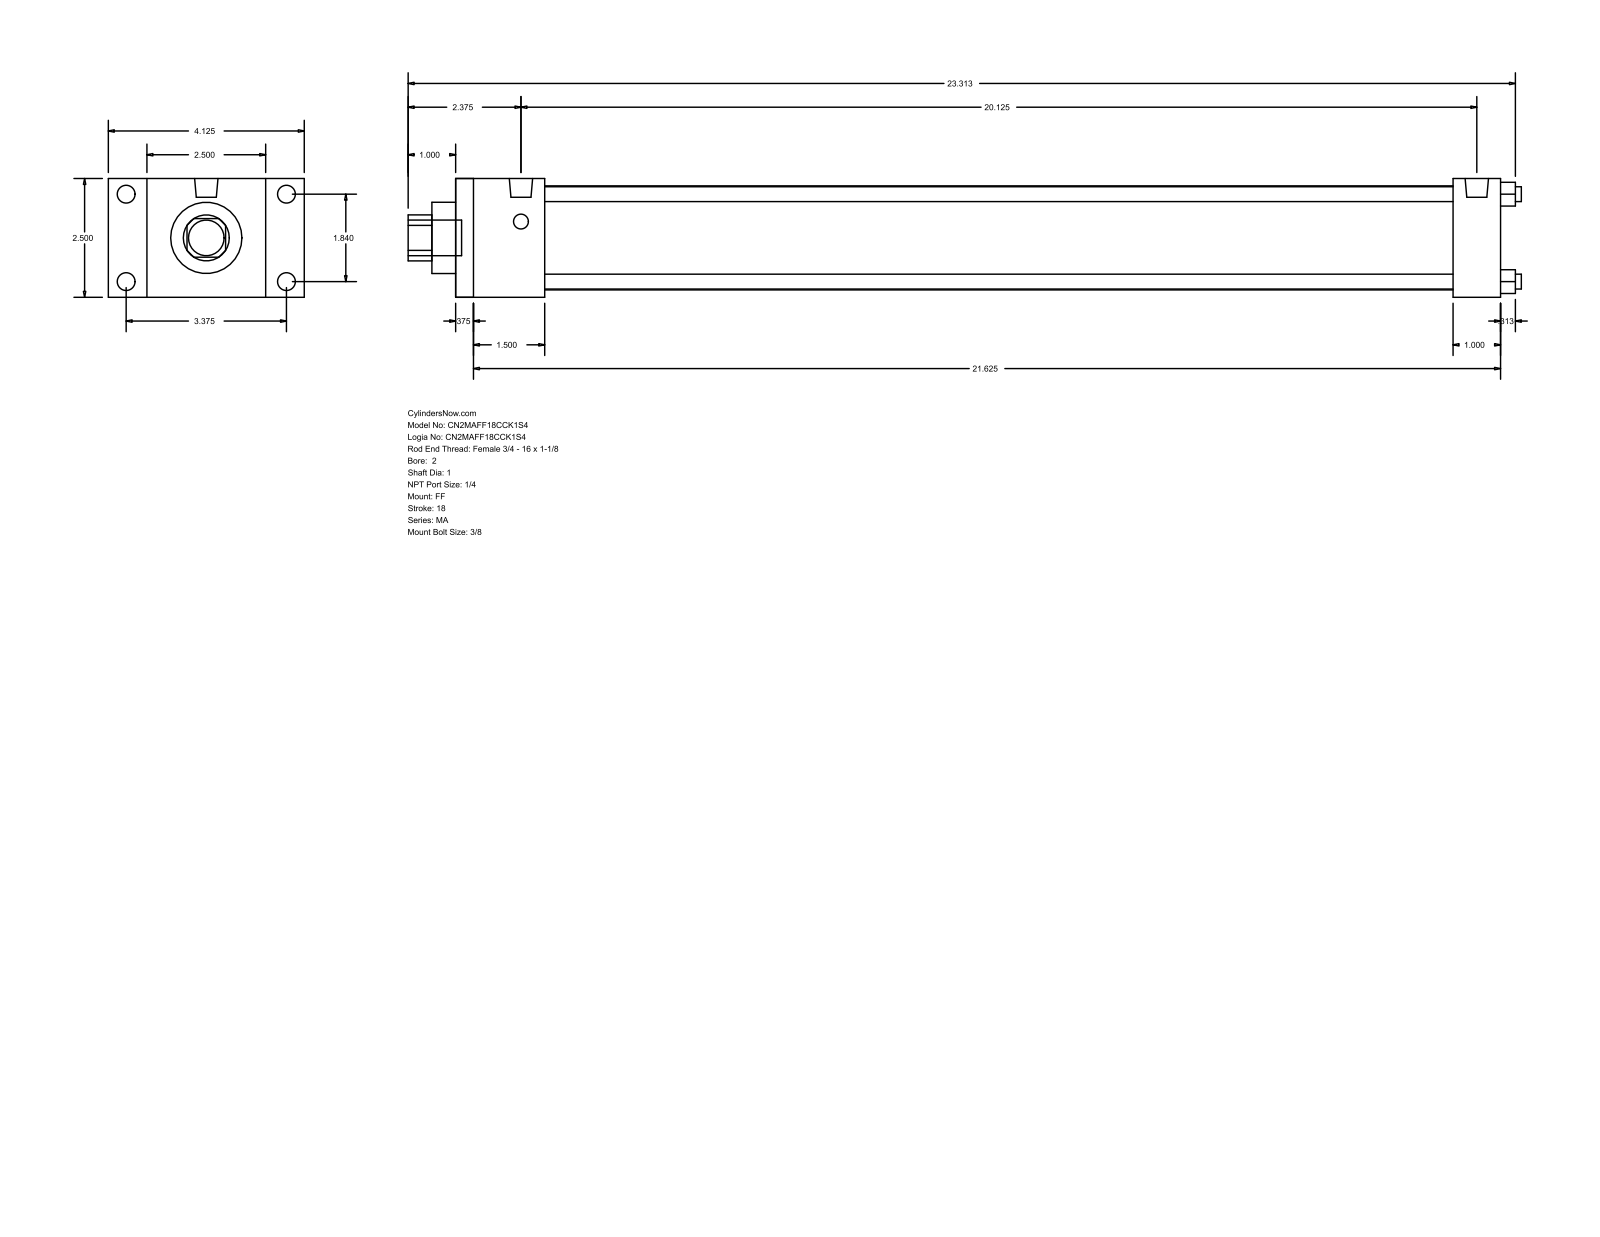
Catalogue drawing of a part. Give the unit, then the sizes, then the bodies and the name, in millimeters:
Units: millimetres
Overall size (bounding box): 595.31 × 104.78 × 63.5
Round holes (diameter × count): ⌀7.94 ×4, ⌀25.4 ×1, ⌀38.1 ×1, ⌀55.63 ×1
Round bosses / shafts (diameter × count): ⌀9.53 ×4, ⌀7.94 ×4, ⌀12.49 ×2, ⌀19.05 ×1
Partial cylindrical surfaces — rounded edges, fillets, slot ends (radius × count): R12.29 ×1
Main face-to-face distances: 63.5, 558.8, 9.52, 549.28, 25.4, 20.64, 12.7, 47.63, 533.4, 38.11
Hole centre spacings: 33.05, 46.74, 66.1
Bodies: 0 solids, 92 faces (64 planar, 28 cylindrical, 0 other)
Part name (STEP PRODUCT): MA_FF__0200_1
STEP written by: GSSL Pune (CONFIG_CONTROL_DESIGN)
